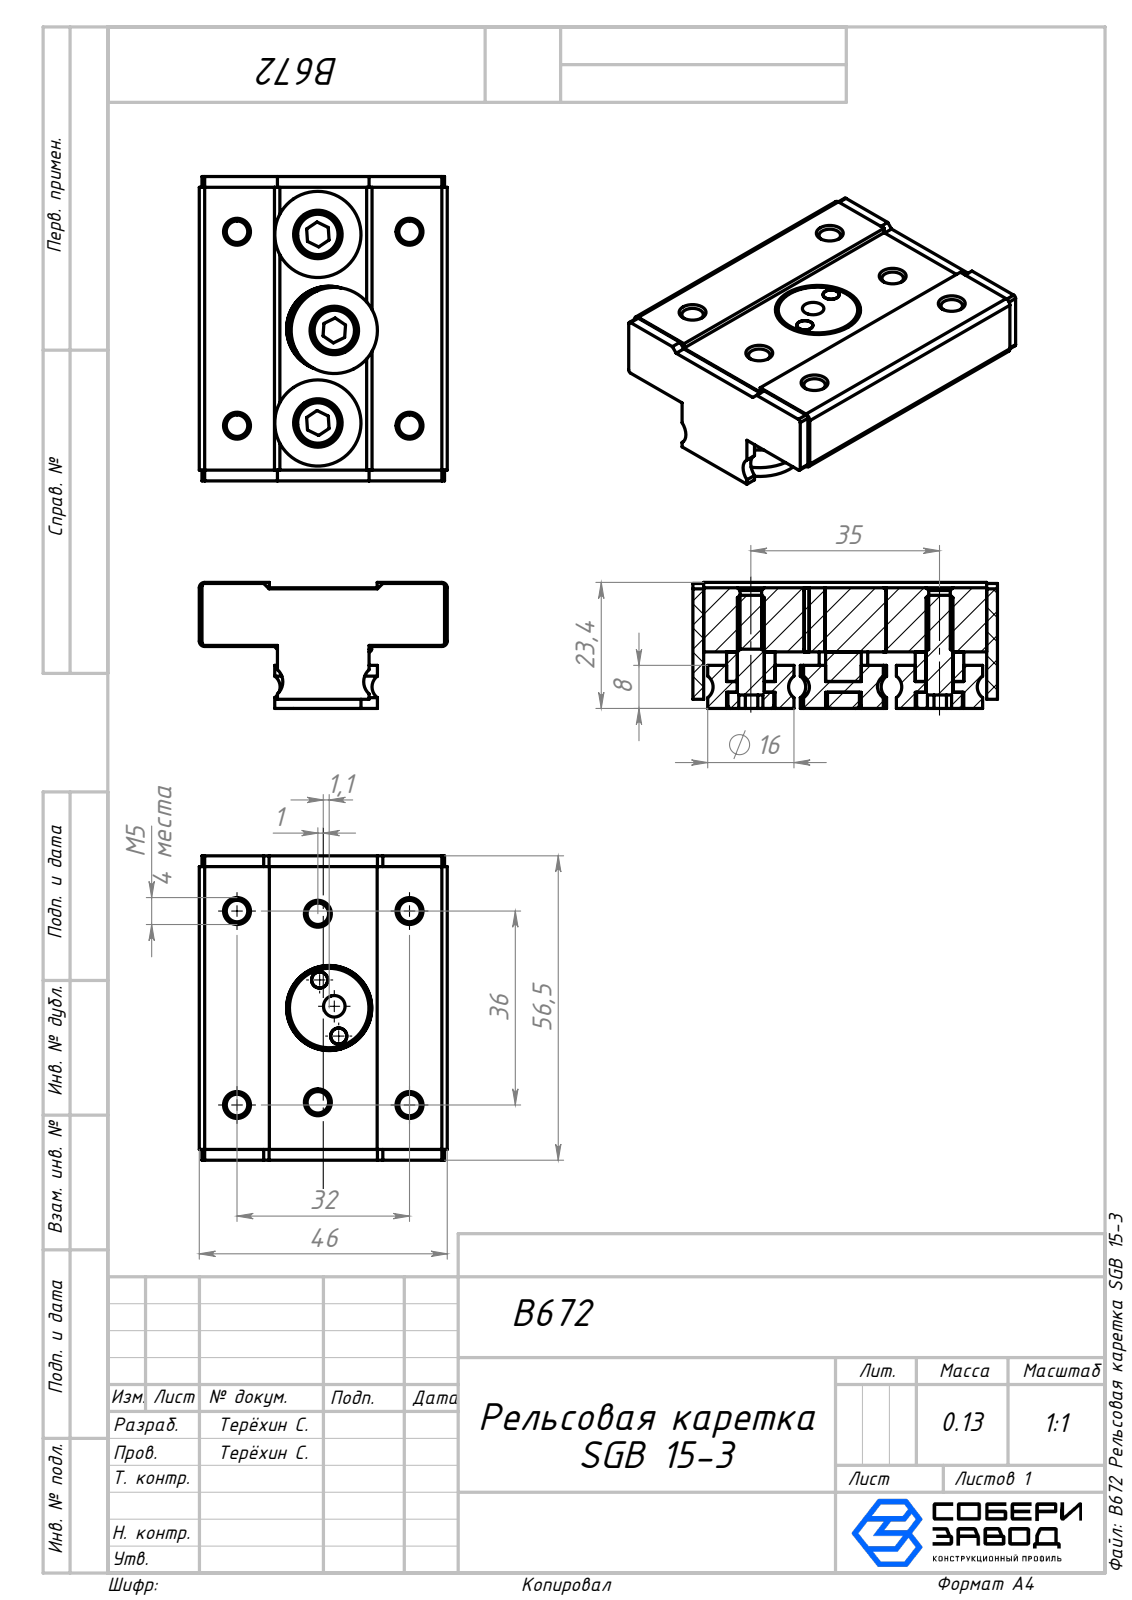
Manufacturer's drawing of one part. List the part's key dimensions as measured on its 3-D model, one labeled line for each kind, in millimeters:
Part name (STEP PRODUCT): B672 Заслонка_00; B672 Дистанционная втулка_00; B672 Деталь для настройки смещения оси_00; B672 Рельсовая каретка SGB 15-3 (+4 more)
STEP written by: SolidWorks 2025 (AUTOMOTIVE_DESIGN)
Units: millimetres
Bodies: 15 solids, 256 faces (100 planar, 98 cylindrical, 58 other)
Overall size (bounding box): 56.5 × 46 × 23.4
Volume: 35 442 mm³ · Surface area: 18 254 mm²
Round holes (diameter × count): ⌀4 ×7, ⌀5 ×3, ⌀9 ×3, ⌀3 ×2, ⌀15.8 ×1
Round bosses / shafts (diameter × count): ⌀16 ×3, ⌀8.5 ×3, ⌀15.75 ×1
Partial cylindrical surfaces — rounded edges, fillets, slot ends (radius × count): R0.5 ×4, R1 ×4, R3.03 ×2
Main face-to-face distances: 11.9, 1, 2, 54.5, 52.5, 10.9, 12.9, 56.5, 10.5, 11.5
Hole centre spacings: 5.5, 15.01, 17.01, 17.63, 23.37, 24.83, 32, 36
